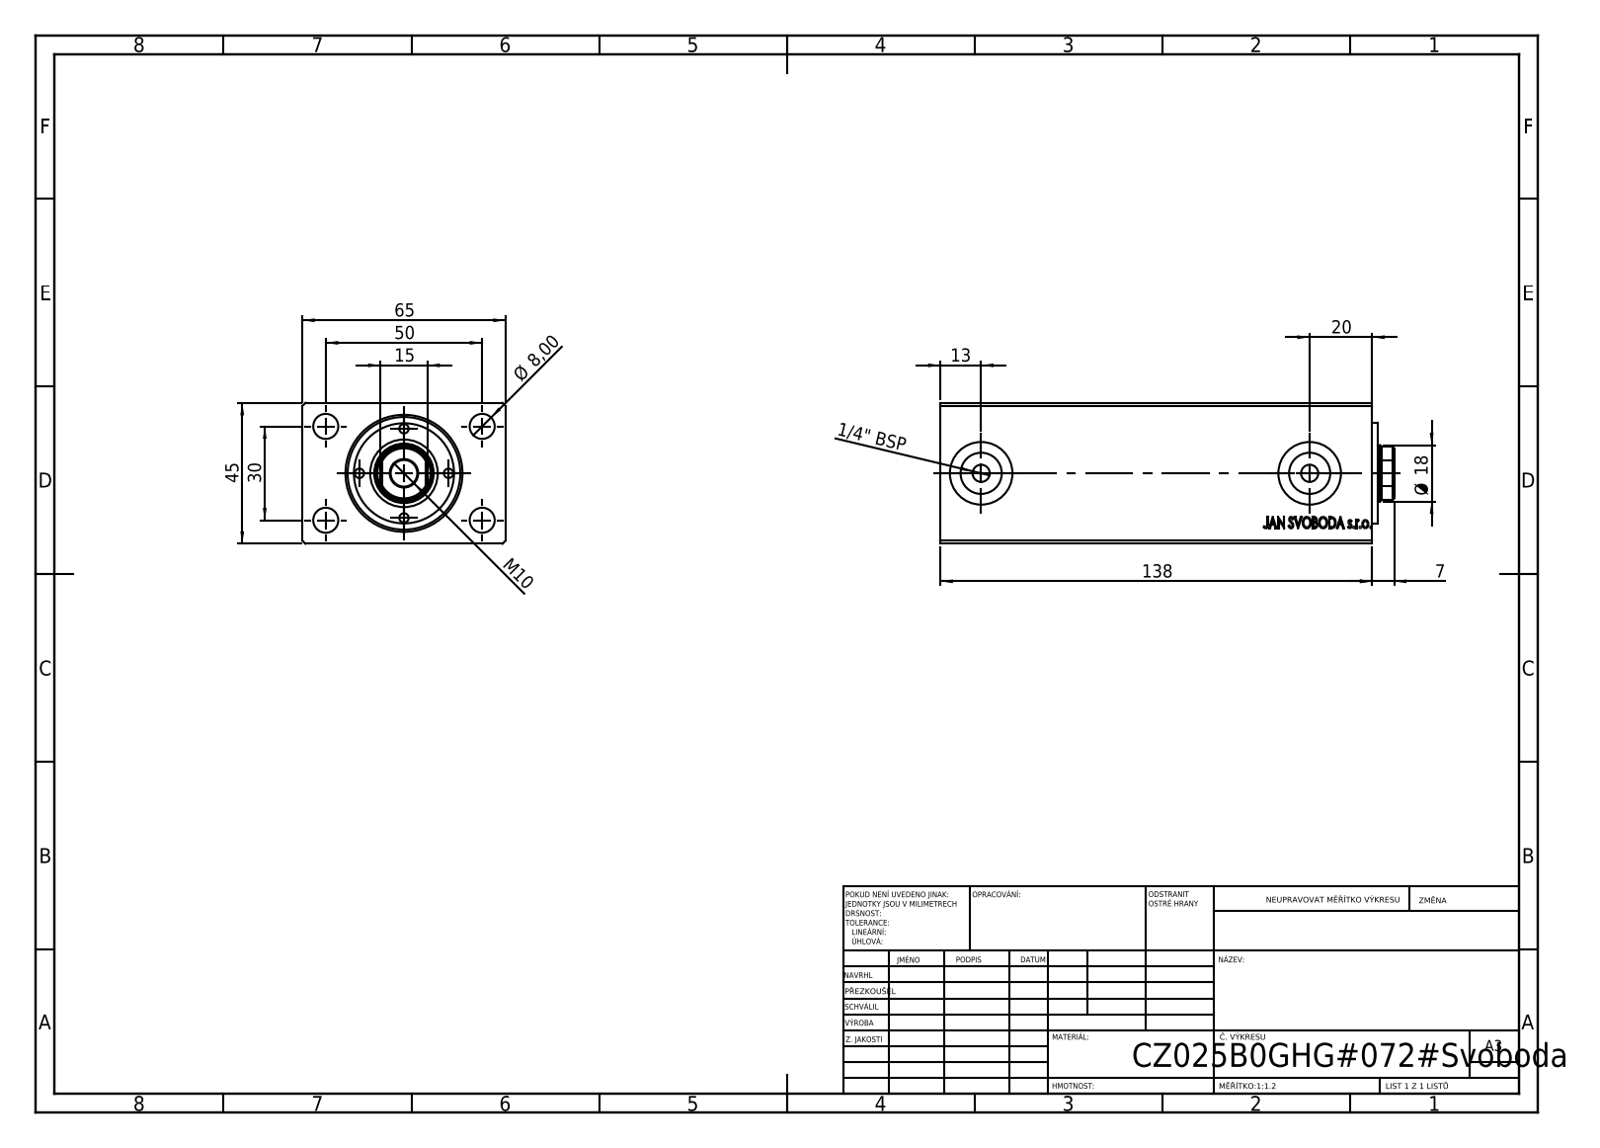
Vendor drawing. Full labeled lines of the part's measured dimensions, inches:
Part name (STEP PRODUCT): V500CZ_B_VC; V500CZ
STEP written by: SolidWorks 2019 (CONFIG_CONTROL_DESIGN)
Units: inches
Bodies: 3 solids, 873 faces (399 planar, 58 cylindrical, 416 other)
Overall size (bounding box): 5.709 × 2.559 × 1.772
Volume: 22.71 in³ · Surface area: 100.6 in²
Round holes (diameter × count): ⌀0.118 ×4, ⌀0.315 ×4, ⌀0.217 ×2, ⌀0.518 ×2, ⌀0.787 ×2, ⌀0.335 ×1, ⌀0.709 ×1, ⌀0.748 ×1, ⌀0.984 ×1, ⌀1.417 ×1
Round bosses / shafts (diameter × count): ⌀1.26 ×1
Partial cylindrical surfaces — rounded edges, fillets, slot ends (radius × count): R0.335 ×1
Main face-to-face distances: 1.772, 2.559, 5.433, 0.276, 5.425, 4.929, 0.496, 0.504, 0.071, 0.205
Hole centre spacings: 0.561, 0.726, 0.793, 0.985, 1.148, 1.515, 1.654, 1.122
